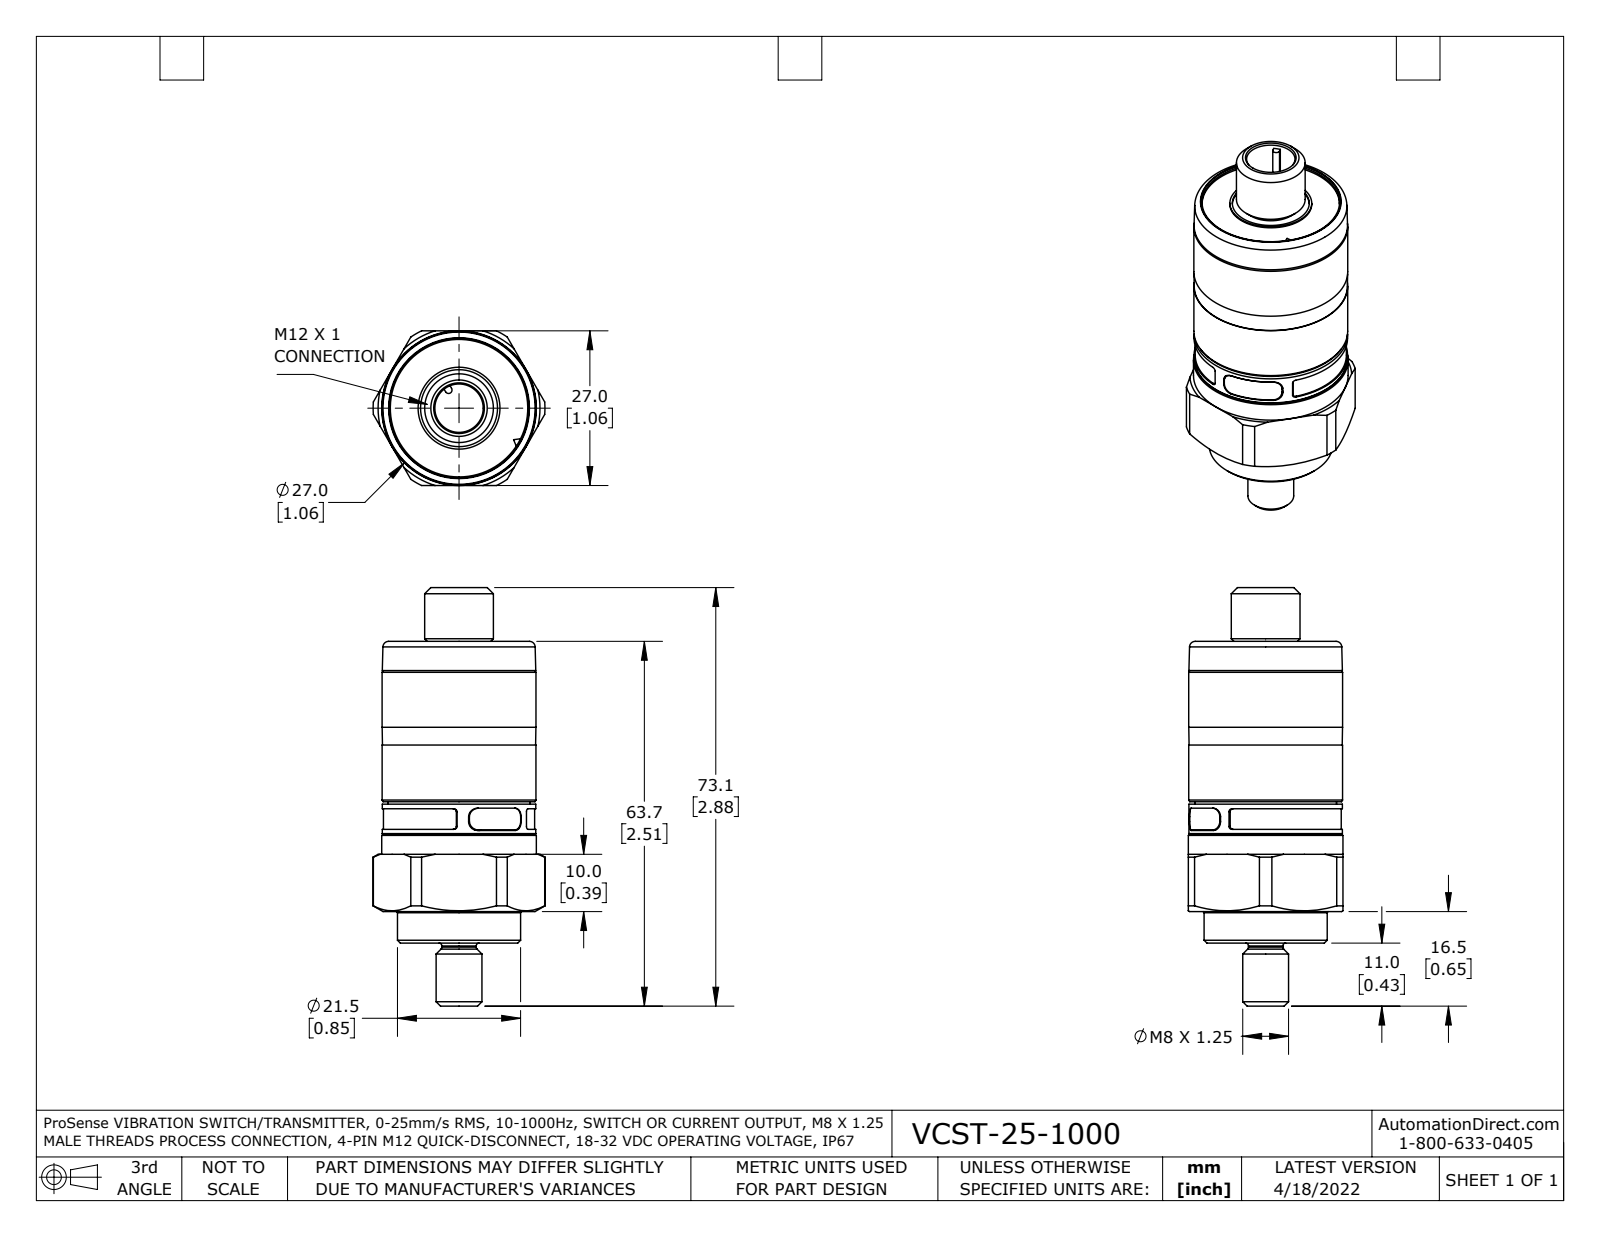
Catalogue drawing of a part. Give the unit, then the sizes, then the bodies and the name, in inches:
Units: inches
Overall size (bounding box): 2.876 × 1.181 × 1.063
Round holes (diameter × count): ⌀0.333 ×1, ⌀0.529 ×1, ⌀0.945 ×1
Round bosses / shafts (diameter × count): ⌀1.063 ×1, ⌀1.058 ×1, ⌀1.057 ×1, ⌀1.055 ×1, ⌀1.039 ×1, ⌀0.974 ×1, ⌀0.846 ×1, ⌀0.563 ×1
Partial cylindrical surfaces — rounded edges, fillets, slot ends (radius × count): R0.059 ×8, R0.02 ×4, R0.024 ×1, R0.528 ×1, R0.591 ×1
Main face-to-face distances: 1.063, 2.052, 0.217, 1.835, 1.278, 0.774, 0.557, 0.778, 0.561, 1.274
Volume: 1.83 in³ · Surface area: 11.03 in²
Bodies: 1 solid, 146 faces (55 planar, 49 cylindrical, 42 other)
Part name (STEP PRODUCT): VCST-25-1000
STEP written by: SolidWorks 2021 (AUTOMOTIVE_DESIGN)
